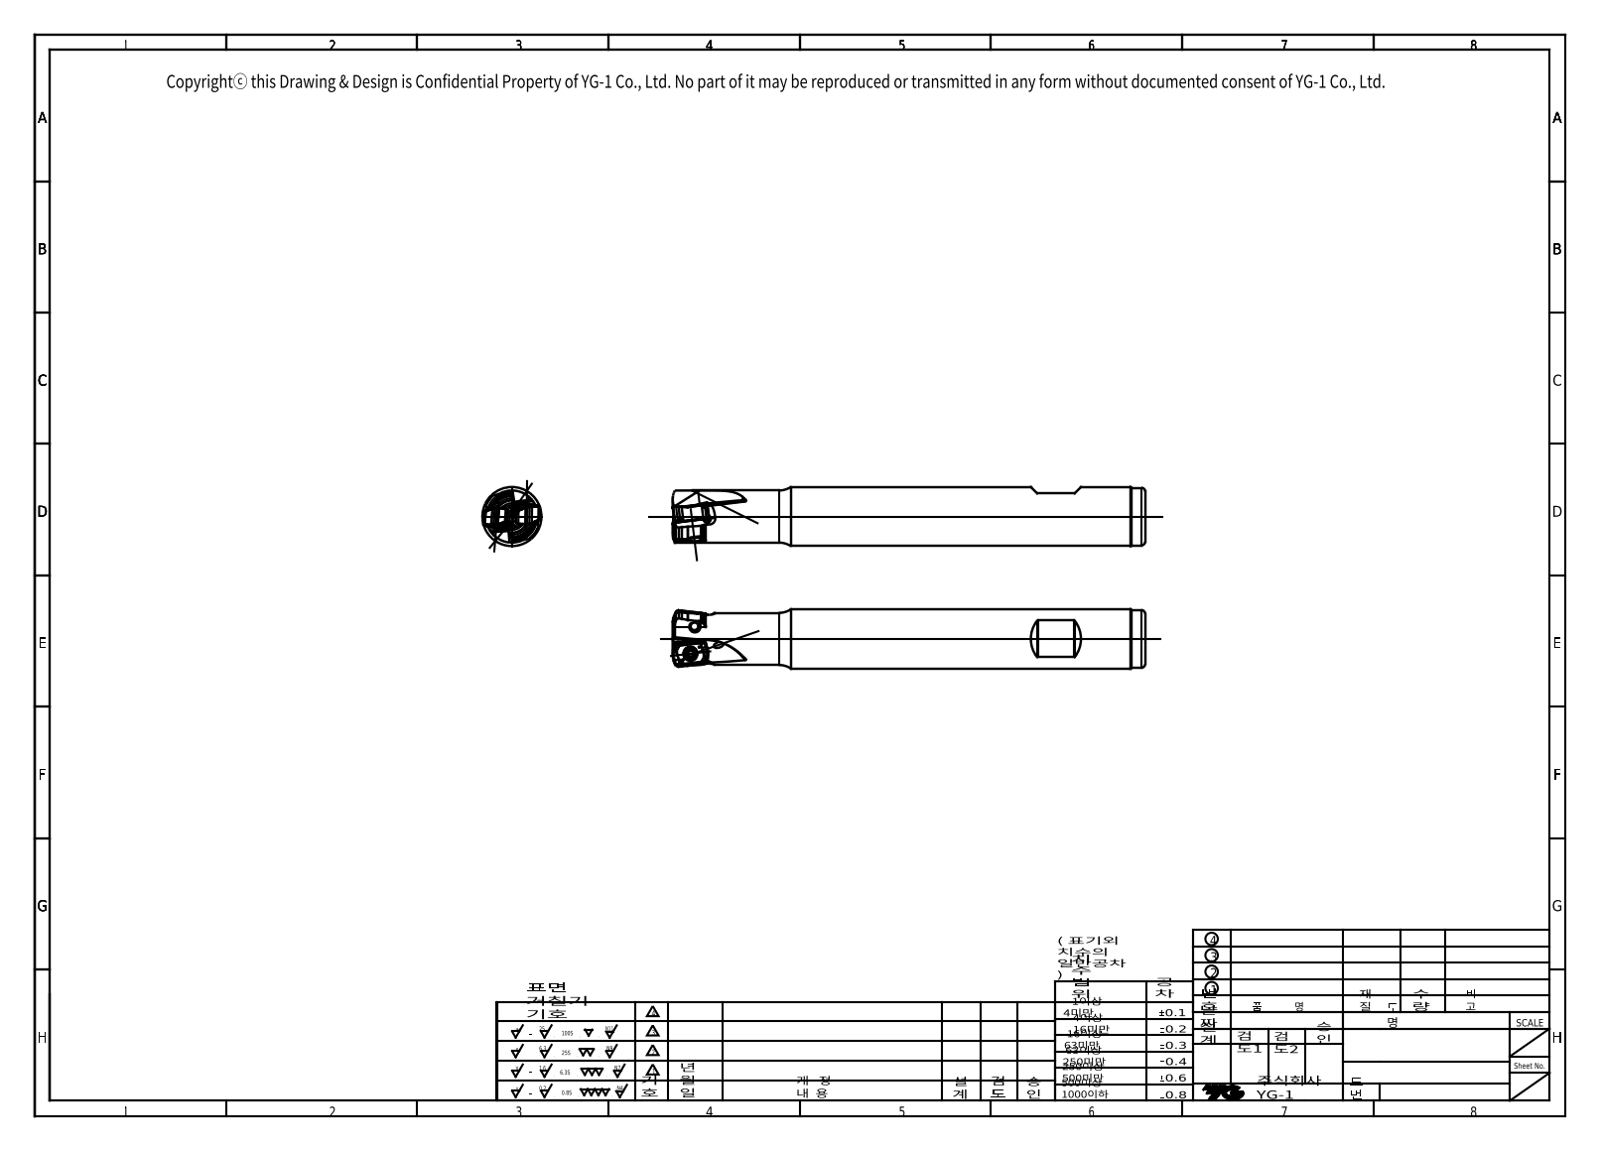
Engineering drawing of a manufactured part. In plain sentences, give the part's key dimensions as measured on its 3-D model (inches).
The part is named "12014C04DDBA1rm6". Its 3-D file was written by "SIEMENS PLM Software NX 10.0 (AP203_CONFIGURATION_CONTROLLED_3D_DESIGN_OF_MECHANICAL_PARTS_AND_ASSEMBLIES_MIM_LF)". It is 2 solids with 49 faces: 5 planar, 6 cylindrical and 38 other. Overall it measures 5 by 0.626 by 0.626 inches. Its volume is 1.11 cubic inches and its surface area 12.78 square inches. Round holes: 1 of diameter 0.197. Round bosses or shafts: 1 of diameter 0.625, 1 of diameter 0.609, 1 of diameter 0.551. Partial cylindrical surfaces (rounded edges, fillets, slot ends): 2 of radius 0.012. The main face-to-face distances are 4.962.
